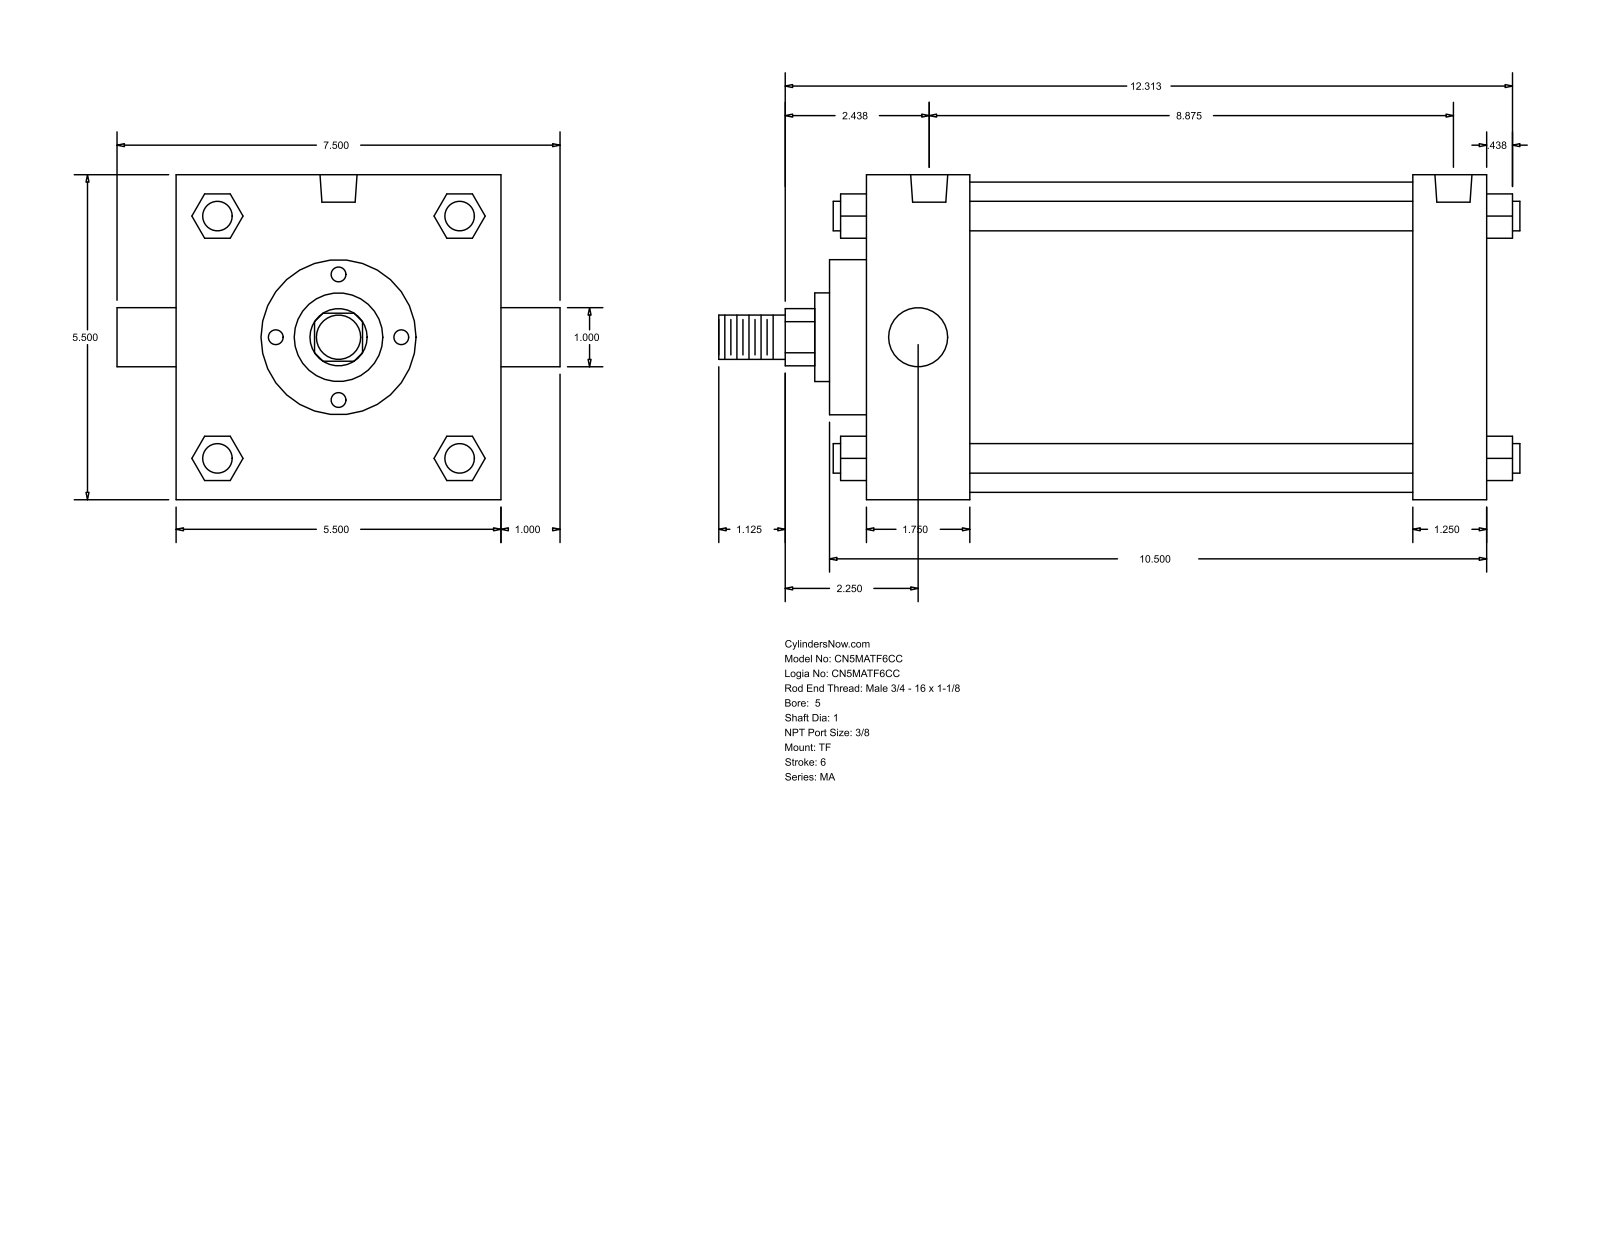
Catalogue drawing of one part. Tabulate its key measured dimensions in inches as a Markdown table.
| quantity | value |
| --- | --- |
| part name | MA_TF__0500_1 |
| STEP written by | GSSL Pune (CONFIG_CONTROL_DESIGN) |
| units | inches |
| bodies | 0 solids, 122 faces (93 planar, 29 cylindrical, 0 other) |
| overall size | 13.563 × 7.5 × 5.5 |
| round holes (diameter × count) | 0.437 × 3, 0.627 × 2 |
| round bosses / shafts (diameter × count) | 0.5 × 4, 1 × 2, 5.25 × 1, 2.625 × 1, 1.5 × 1, 0.75 × 1 |
| partial cylindrical surfaces (radius × count) | 0.484 × 1 |
| main face-to-face distances | 5.5, 10.5, 7.5, 9.25, 1.25, 1.75, 8.75, 0.625, 2.375, 9.875 |
| hole center spacings | 0.187, 0.188, 8.5, 8.687, 8.688, 8.875 |
